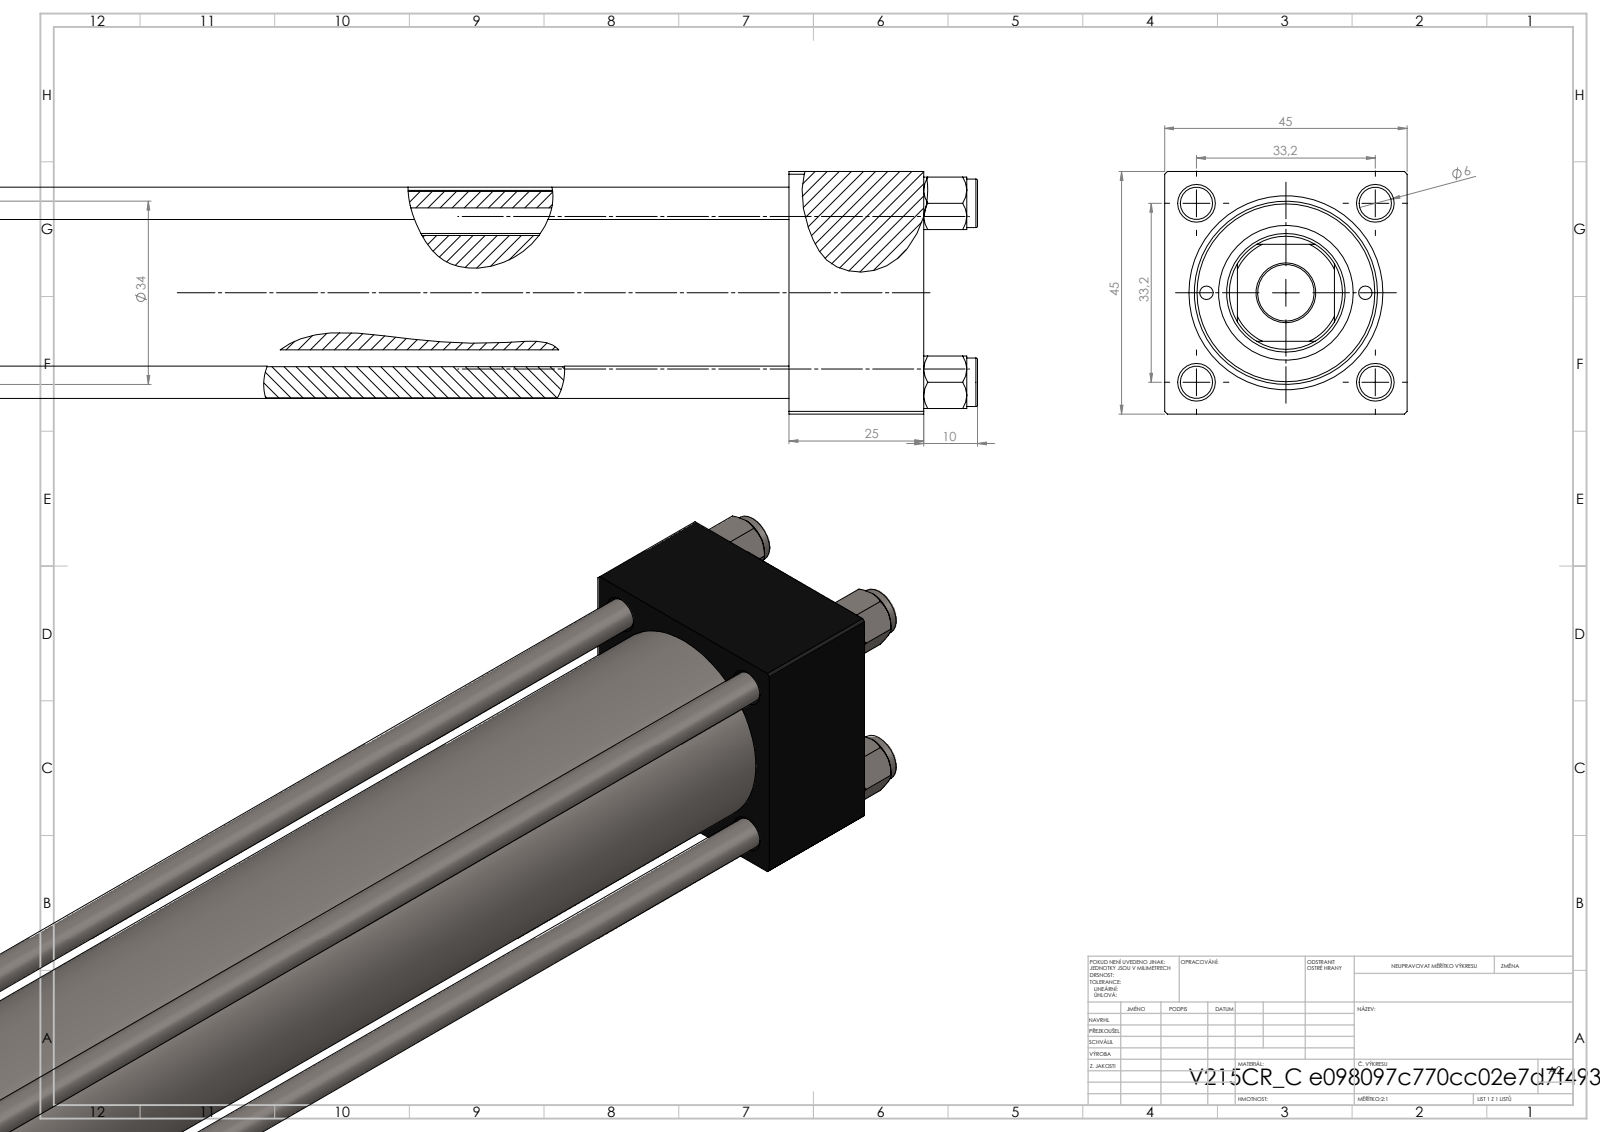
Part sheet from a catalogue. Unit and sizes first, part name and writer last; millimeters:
Units: millimetres
Overall size (bounding box): 338 × 45 × 45
Round holes (diameter × count): ⌀6 ×4, ⌀2.5 ×2, ⌀7 ×2, ⌀13.16 ×2, ⌀20 ×2, ⌀10.5 ×1, ⌀22 ×1, ⌀24 ×1, ⌀25 ×1, ⌀32 ×1, ⌀33 ×1
Round bosses / shafts (diameter × count): ⌀9 ×4, ⌀38 ×1, ⌀34 ×1
Partial cylindrical surfaces — rounded edges, fillets, slot ends (radius × count): R10.5 ×1
Main face-to-face distances: 45, 25, 303, 255, 230, 278, 48, 274.3, 249.3, 19.3
Hole centre spacings: 16.7, 23.48, 33.2, 35.47, 14.75, 46.95, 29.5, 255.5
Volume: 357 850 mm³ · Surface area: 137 166 mm²
Bodies: 11 solids, 1153 faces (527 planar, 90 cylindrical, 536 other)
Part name (STEP PRODUCT): V215_VC_A; NUT_M5_C; V215CR_C_Body; V215CR_C_TYCINKA (+1 more)
STEP written by: SolidWorks 2019 (CONFIG_CONTROL_DESIGN)
